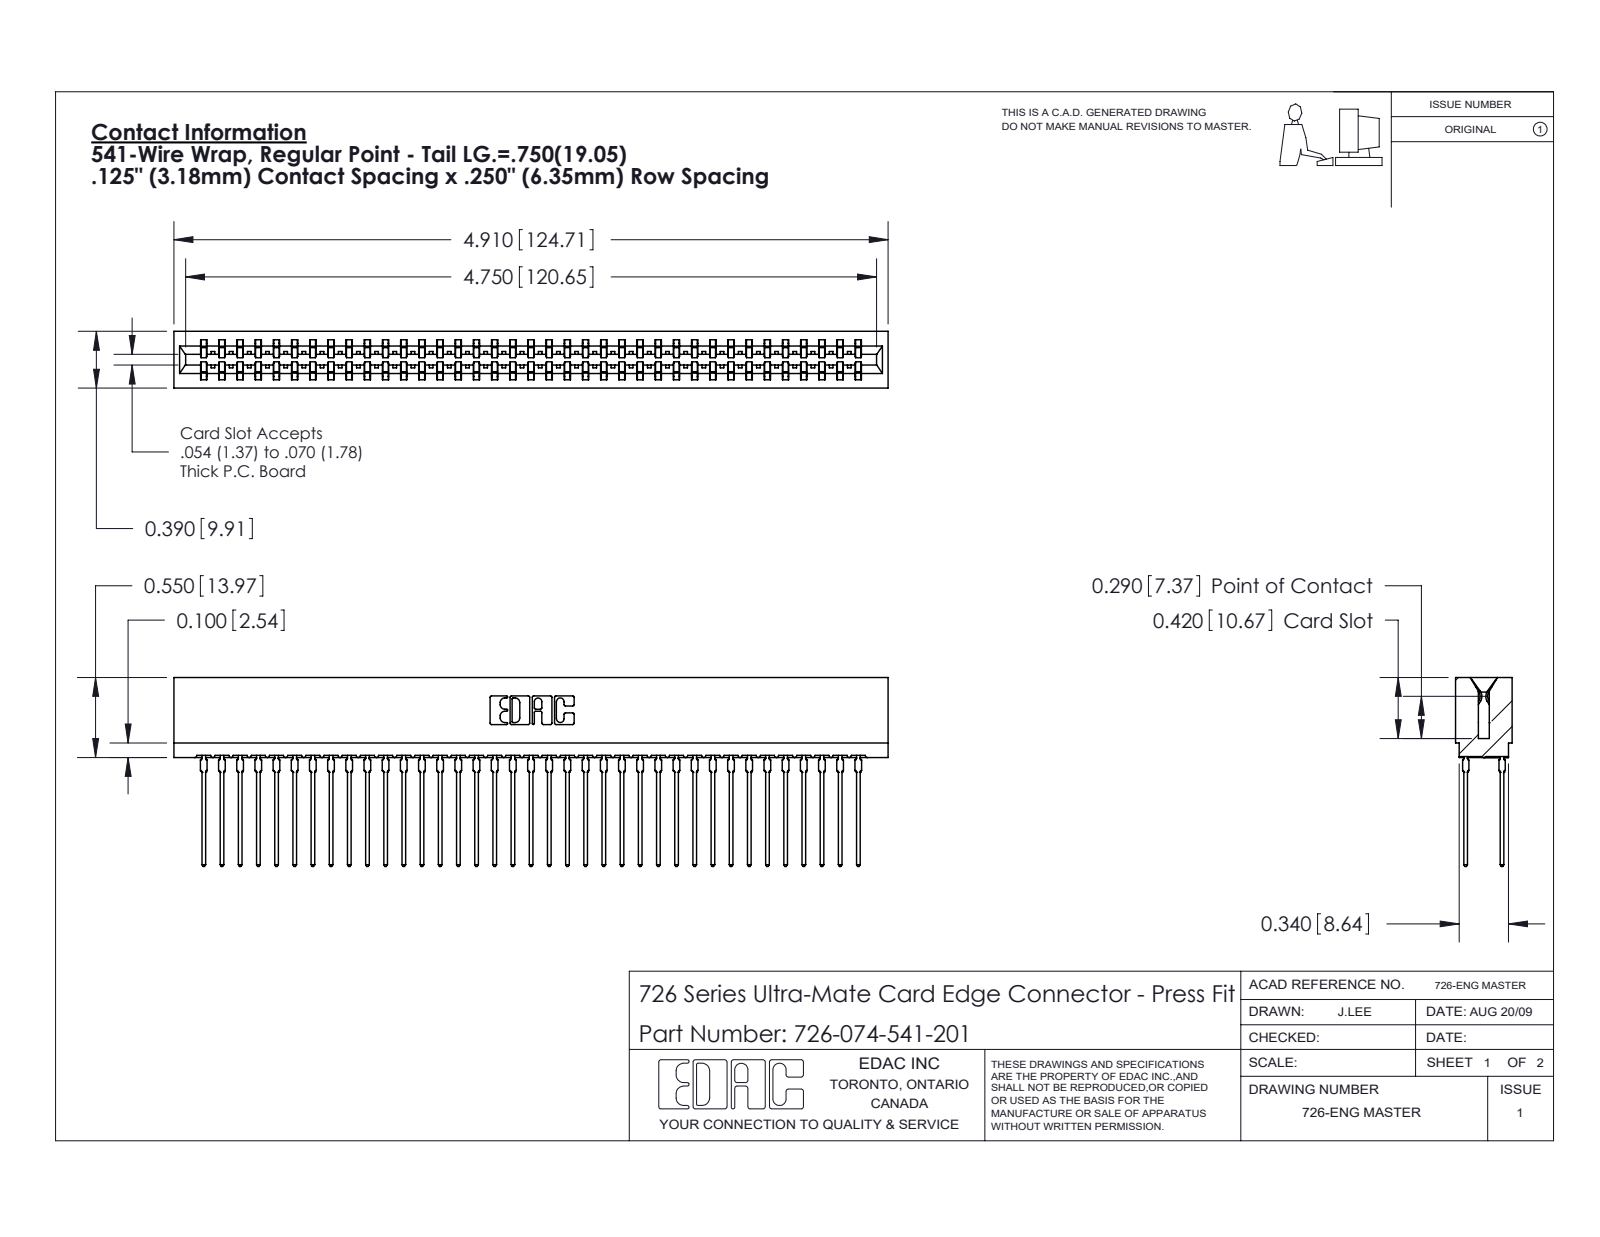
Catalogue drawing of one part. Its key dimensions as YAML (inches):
part_name: "746-292-001_541; 726 Part_.515 Slot Depth - 01; 726-074-541-201"
step_written_by: "SolidWorks 2020 (CONFIG_CONTROL_DESIGN)"
units: inches
bodies: {solids: 75, faces: 6720, planar: 3459, cylindrical: 1337, other: 1924}
overall_size: [4.91, 1.299, 0.39]
volume: 0.727
surface_area: 33.55
partial_cylinders:
  - {radius: 0.021, count: 148}
  - {radius: 0.015, count: 38}
  - {radius: 0.01, count: 22}
  - {radius: 0.005, count: 8}
  - {radius: 0.011, count: 8}
  - {radius: 0.007, count: 6}
  - {radius: 0.031, count: 6}
  - {radius: 0.026, count: 3}
face_to_face_distances: [0.057, 0.333, 0.25, 0.025, 0.307, 0.39, 0.083, 0.275, 0.5, 0.225]
